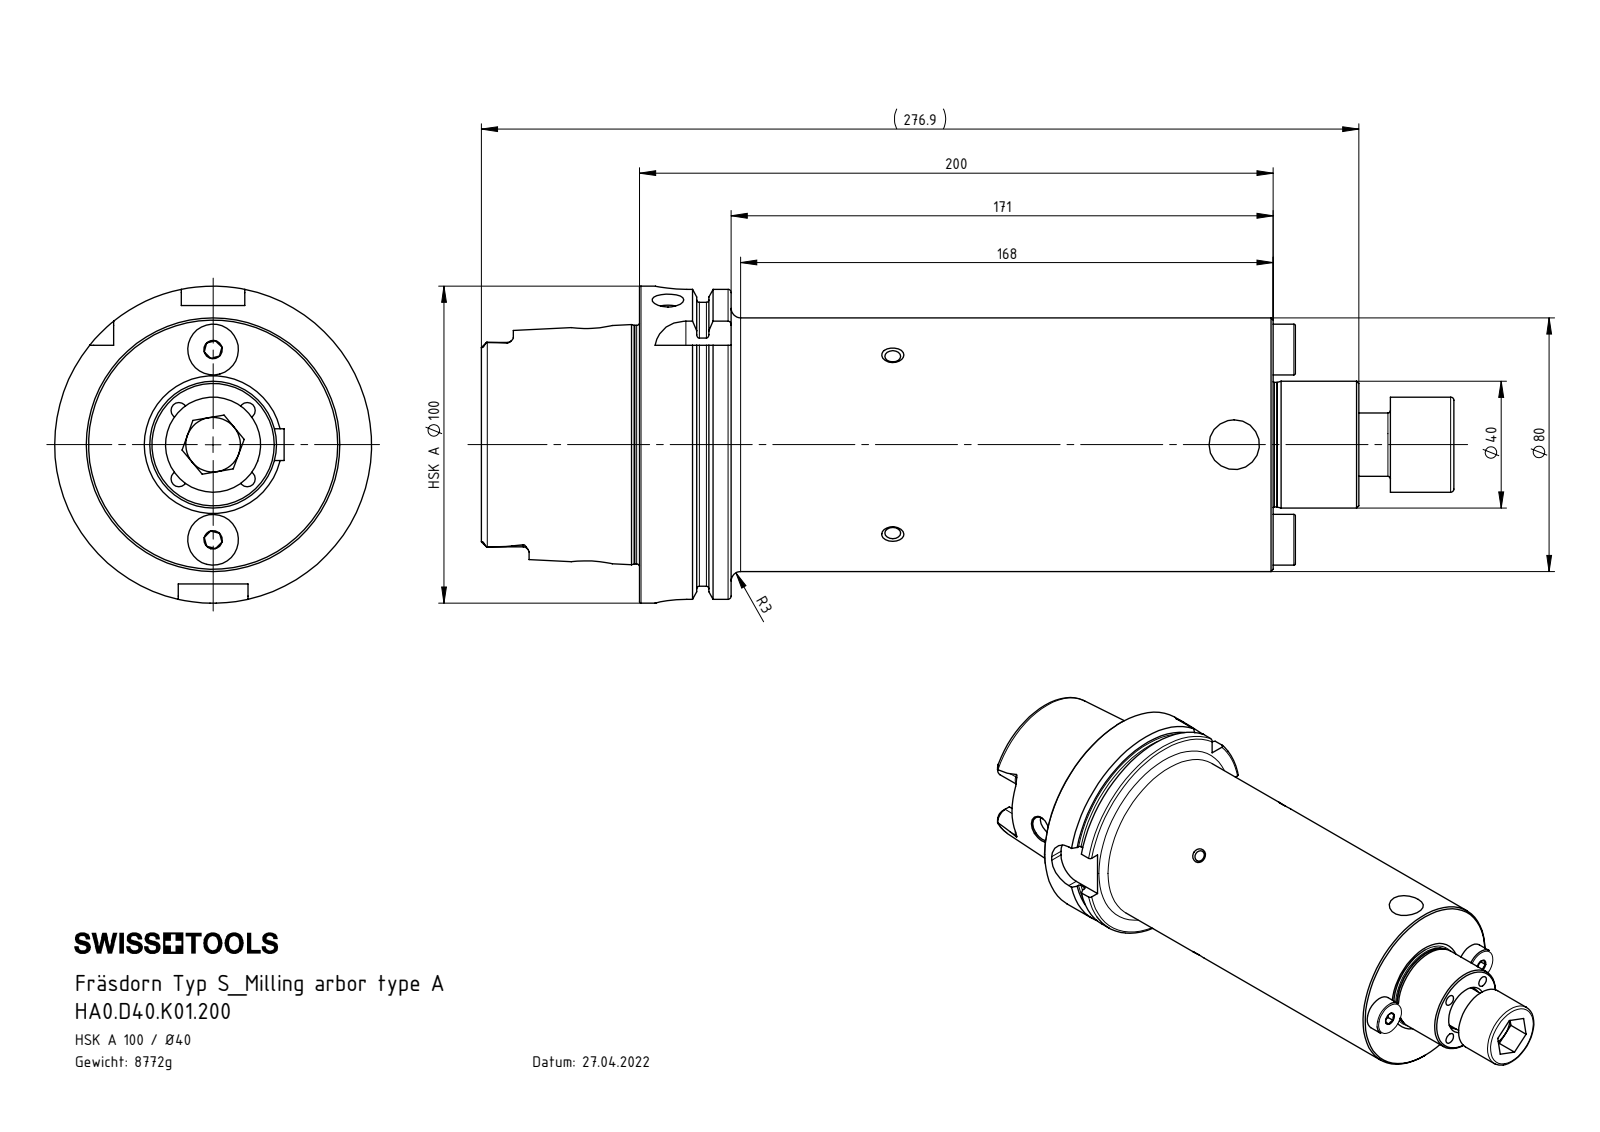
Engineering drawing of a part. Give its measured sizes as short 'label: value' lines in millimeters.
name: HA0.D40.K01.200; ISO 4762 - M20 x 40; D40-ER2.001.023_B; HA0-D40.K01.200_A_Fertigbearbeitung (+1 more)
written by: SolidWorks 2017 (AUTOMOTIVE_DESIGN)
unit: mm
bodies: 4 solids, 116 faces (39 planar, 25 cylindrical, 52 other)
size: 225.05 × 80 × 80
volume: 30 070 mm³; area: 51 314 mm²
bosses: 2× ⌀16, 2× ⌀14, 2× ⌀6, 2× ⌀4.6, 1× ⌀80, 1× ⌀30, 1× ⌀20
rounds: 2× R5
face distances: 10, 20, 50, 3, 30, 40, 13, 63, 60, 43
